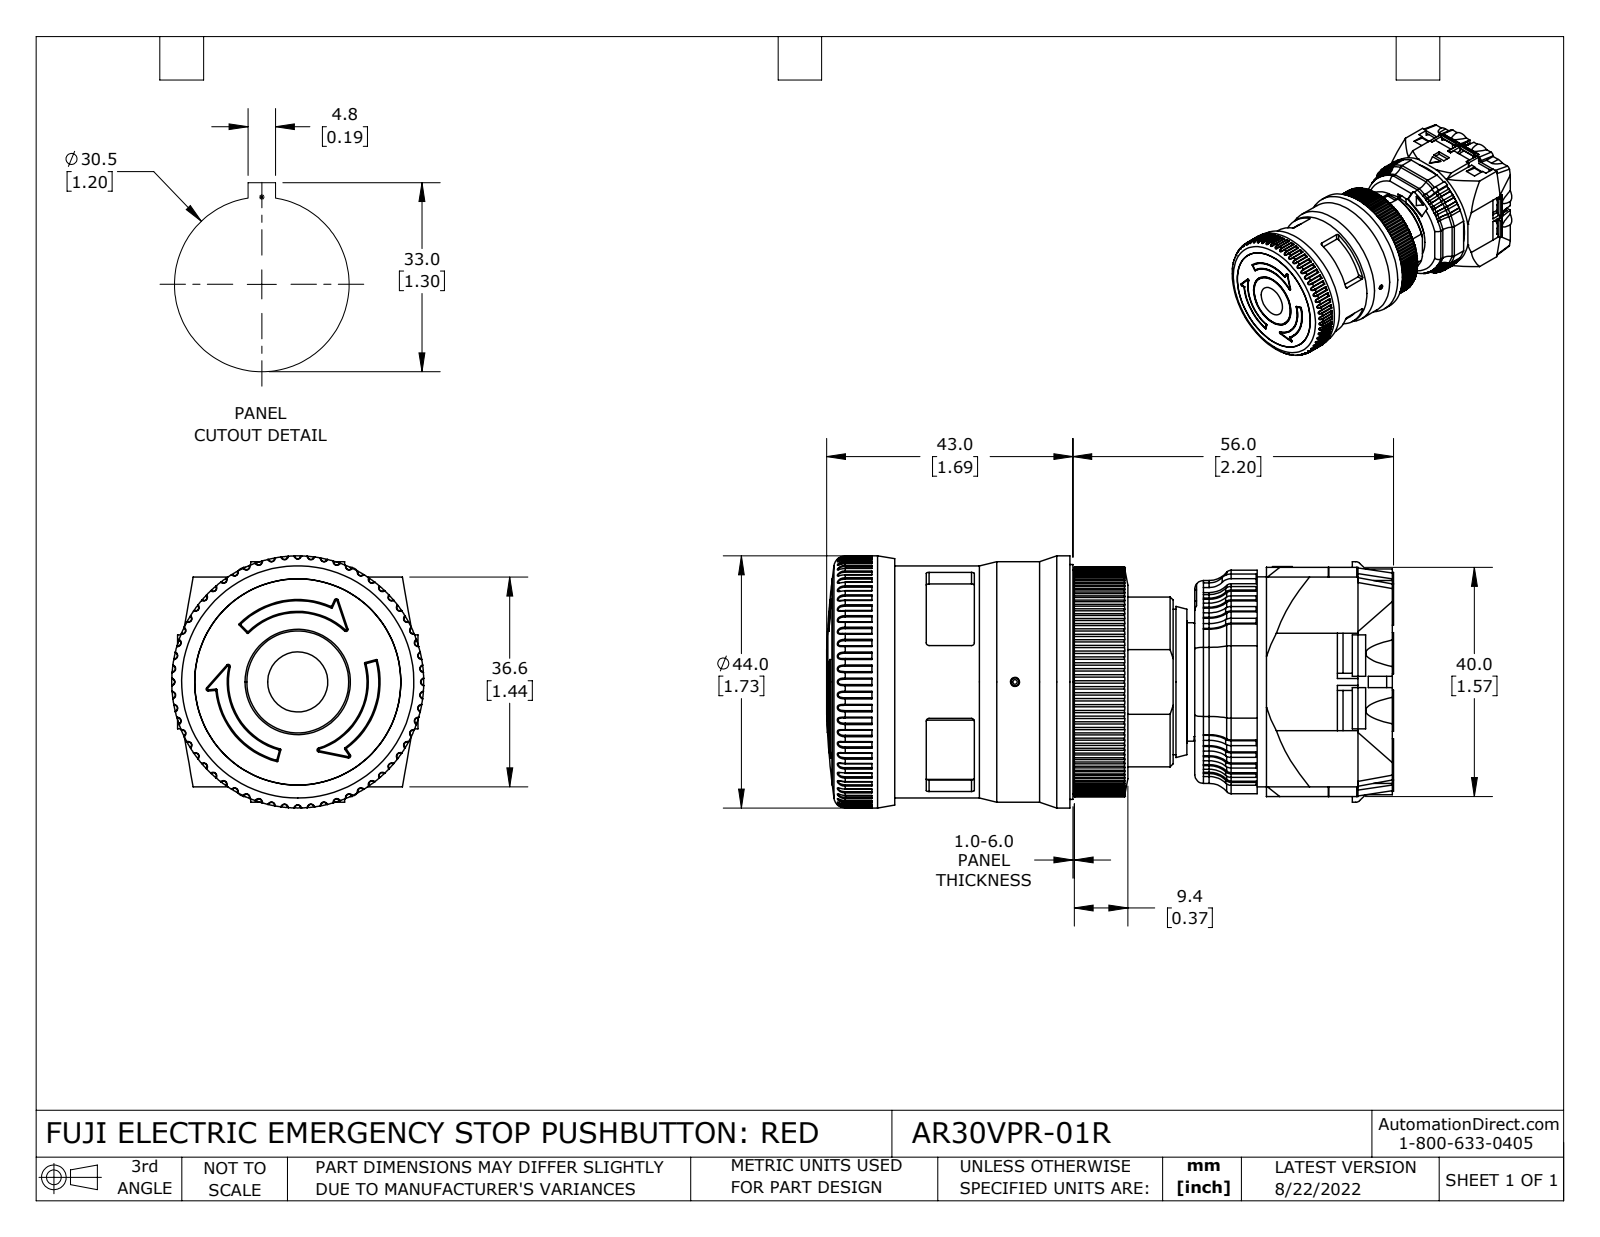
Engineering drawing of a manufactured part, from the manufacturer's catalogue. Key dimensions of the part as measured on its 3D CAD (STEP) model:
Part name (STEP PRODUCT): AR30VPR-01R
STEP written by: SolidWorks 2021 (CONFIG_CONTROL_DESIGN)
Units: inches
Bodies: 32 solids, 2480 faces (1039 planar, 1119 cylindrical, 322 other)
Overall size (bounding box): 3.898 × 1.732 × 1.732
Volume: 6.151 in³ · Surface area: 109.1 in²
Round holes (diameter × count): ⌀0.138 ×12, ⌀0.244 ×12, ⌀0.13 ×2, ⌀0.031 ×1, ⌀0.063 ×1, ⌀0.26 ×1, ⌀0.315 ×1, ⌀0.689 ×1, ⌀0.693 ×1, ⌀0.724 ×1, ⌀0.827 ×1, ⌀0.843 ×1
Round bosses / shafts (diameter × count): ⌀0.283 ×12, ⌀1.732 ×1, ⌀1.654 ×1, ⌀1.614 ×1, ⌀1.535 ×1, ⌀1.417 ×1, ⌀1.299 ×1, ⌀1.291 ×1
Partial cylindrical surfaces — rounded edges, fillets, slot ends (radius × count): R0.008 ×120, R0.013 ×120, R0.02 ×76, R0.005 ×24, R0.049 ×19, R0.148 ×19, R0.039 ×15, R0.059 ×12
Main face-to-face distances: 0.118, 1.48, 0.039, 0.839, 1.598, 0.102, 1.516, 1.496, 1.378, 0.339
Hole centre spacings: 0.641, 0.907, 0.325, 0.349, 0.394, 0.585, 0.713, 0.735
